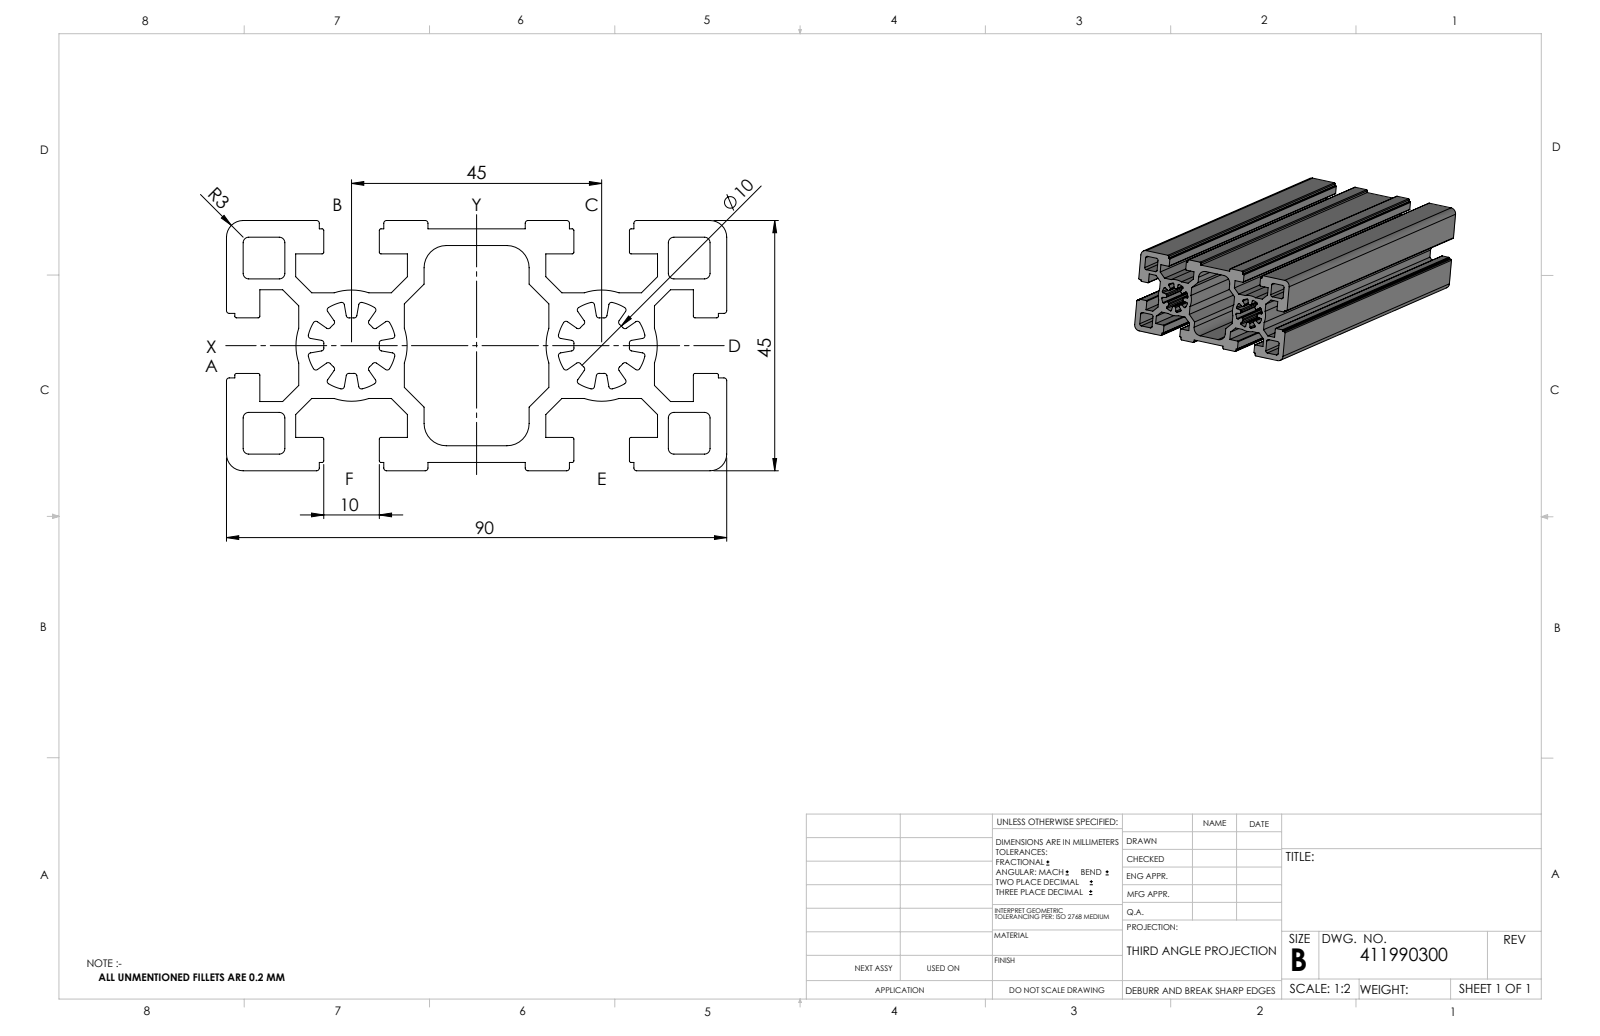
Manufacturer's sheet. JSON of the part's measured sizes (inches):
{"part_name": "411990300_c_1", "step_written_by": "SolidWorks 2014 (CONFIG_CONTROL_DESIGN)", "units": "inches", "bodies": {"solids": 1, "faces": 354, "planar": 166, "cylindrical": 188, "other": 0}, "overall_size": [7.874, 3.543, 1.772], "volume_in3": 18.6, "surface_area_in2": 286.9, "partial_cylinders_radius": [[0.02, 80], [0.012, 24], [0.039, 16], [0.118, 4], [0.157, 4], [0.197, 2], [0.315, 2], [0.394, 2]], "face_to_face_distances": [0.177, 0.118, 0.059, 1.772, 0.276, 0.236, 0.571, 1.024, 1.535, 0.846]}
